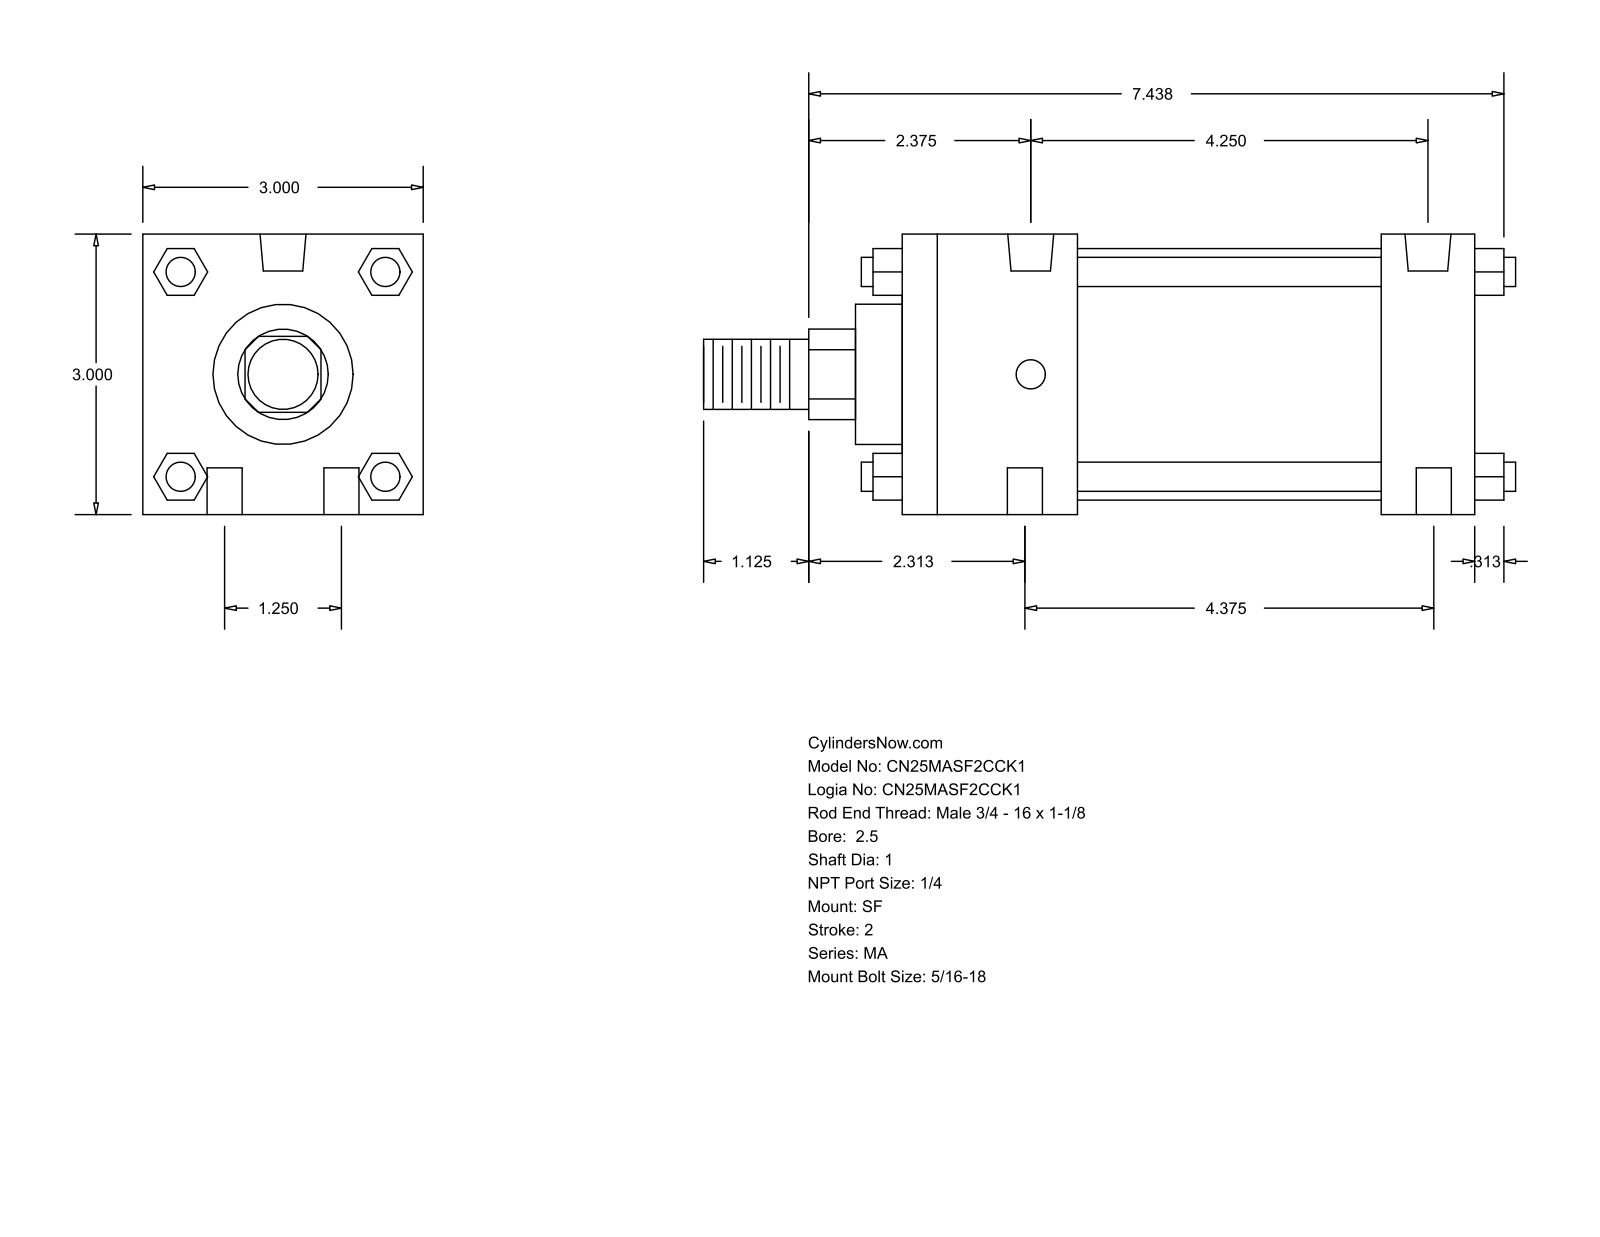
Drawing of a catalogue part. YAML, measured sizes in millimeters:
part_name: "MA_SF__0250_1"
step_written_by: "GSSL Pune (CONFIG_CONTROL_DESIGN)"
units: millimeters
bodies: {solids: 0, faces: 124, planar: 94, cylindrical: 30, other: 0}
overall_size: [220.66, 76.2, 76.2]
round_holes:
  - {diameter: 9.53, count: 4}
  - {diameter: 7.94, count: 2}
  - {diameter: 12.49, count: 2}
round_bosses_or_shafts:
  - {diameter: 7.94, count: 4}
  - {diameter: 68.33, count: 1}
  - {diameter: 38.1, count: 1}
  - {diameter: 25.4, count: 1}
  - {diameter: 19.05, count: 1}
partial_cylinders:
  - {radius: 12.29, count: 1}
face_to_face_distances: [76.2, 155.57, 12.7, 25.4, 130.17, 47.63, 82.54, 107.94, 27.81, 48.17]
hole_center_spacings: [15.96, 31.76, 107.95, 110.68, 110.69, 111.12, 115.57]
